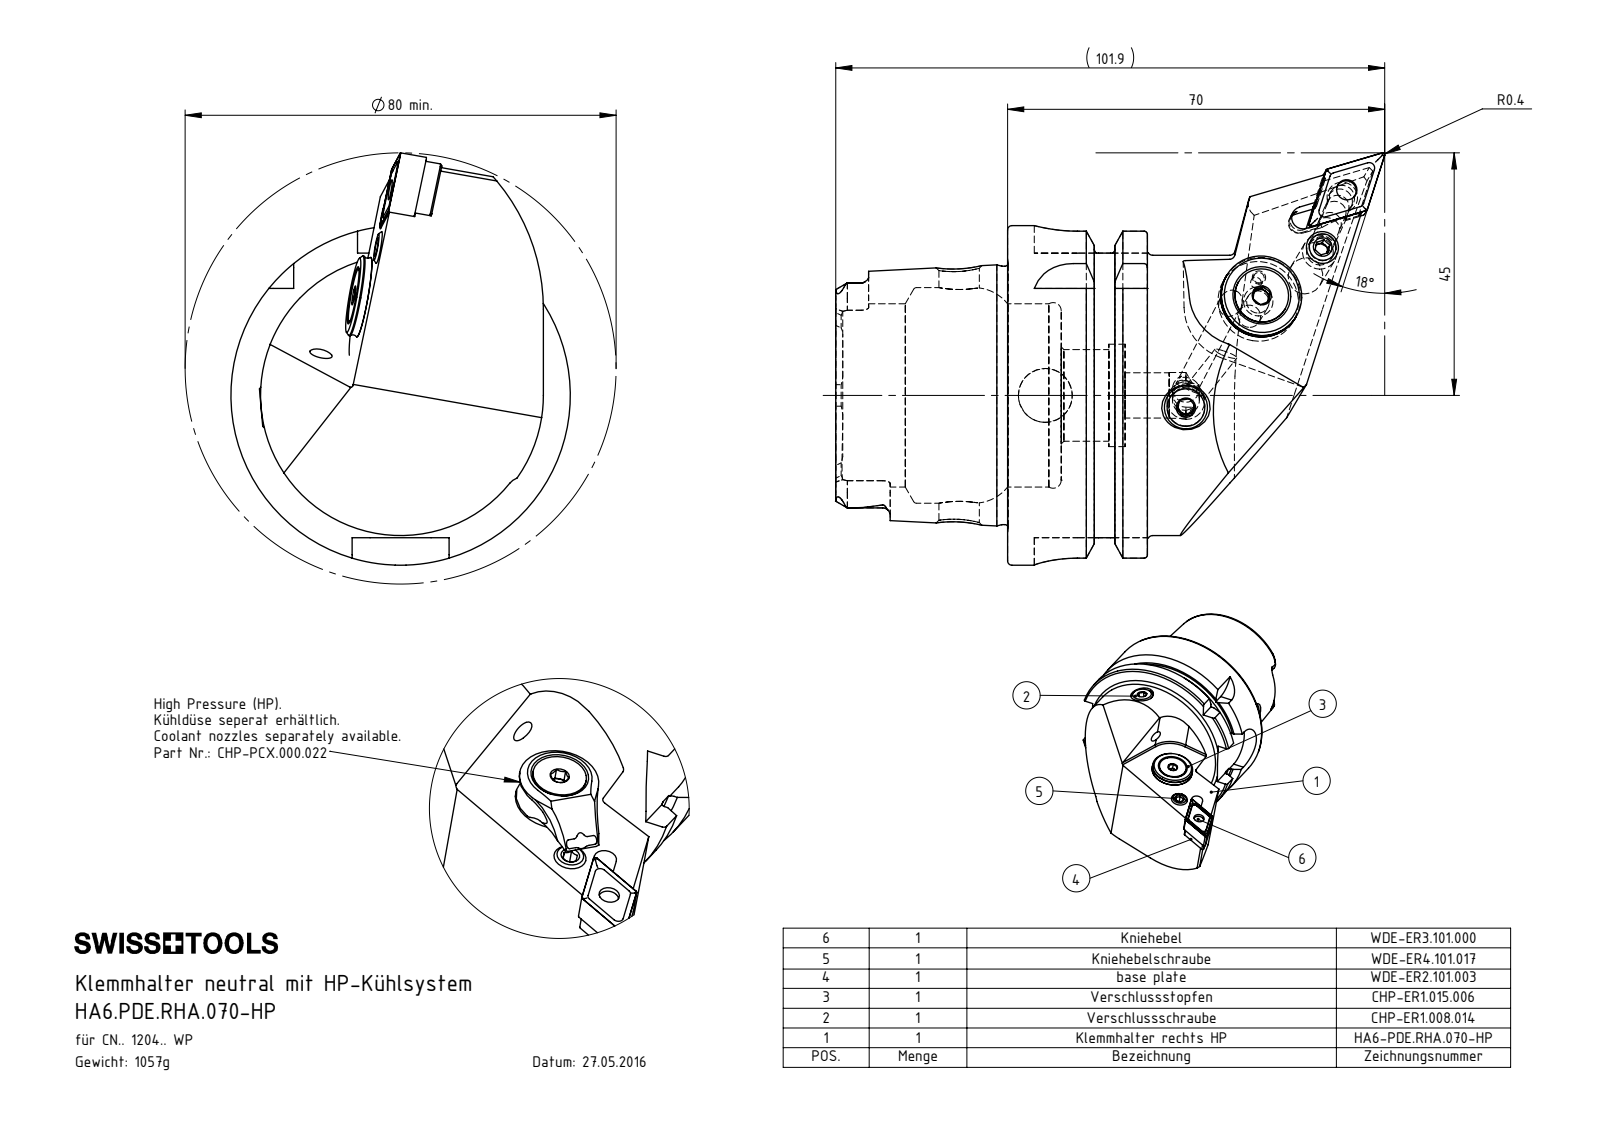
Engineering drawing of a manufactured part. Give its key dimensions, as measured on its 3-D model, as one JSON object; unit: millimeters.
{"part_name": "WDE-ER1.101.000; CHP-ER1.008.014_A; DIN 7991 - M5x15; WDE-ER3.101.000_A (+8 more)", "step_written_by": "SolidWorks 2017 (AUTOMOTIVE_DESIGN)", "units": "millimeters", "bodies": {"solids": 11, "faces": 395, "planar": 176, "cylindrical": 84, "other": 135}, "overall_size": [101.91, 76.5, 63], "volume_mm3": 134785, "surface_area_mm2": 33343, "round_holes": [[4.2, 3], [2.5, 2], [5, 2], [1.2, 1], [2, 1], [3, 1], [3.81, 1], [4.8, 1], [5.2, 1], [6.4, 1], [7, 1], [7.5, 1]], "round_bosses_or_shafts": [[63, 1], [54.95, 1], [52, 1], [47.94, 1], [15, 1], [13.4, 1], [10, 1], [8, 1]], "partial_cylinders_radius": [[0.4, 8], [1.4, 6], [2.1, 5], [2.88, 4], [8, 4], [0.5, 2], [1.81, 1], [1.85, 1]], "face_to_face_distances": [25.95, 16, 9.95, 31.9, 41.85, 57.85, 52.8, 21.8, 11.85, 4.5], "hole_center_spacings": [12.45, 14.97, 14.98, 26.11, 4.5, 4.51, 4.52, 4.53]}
